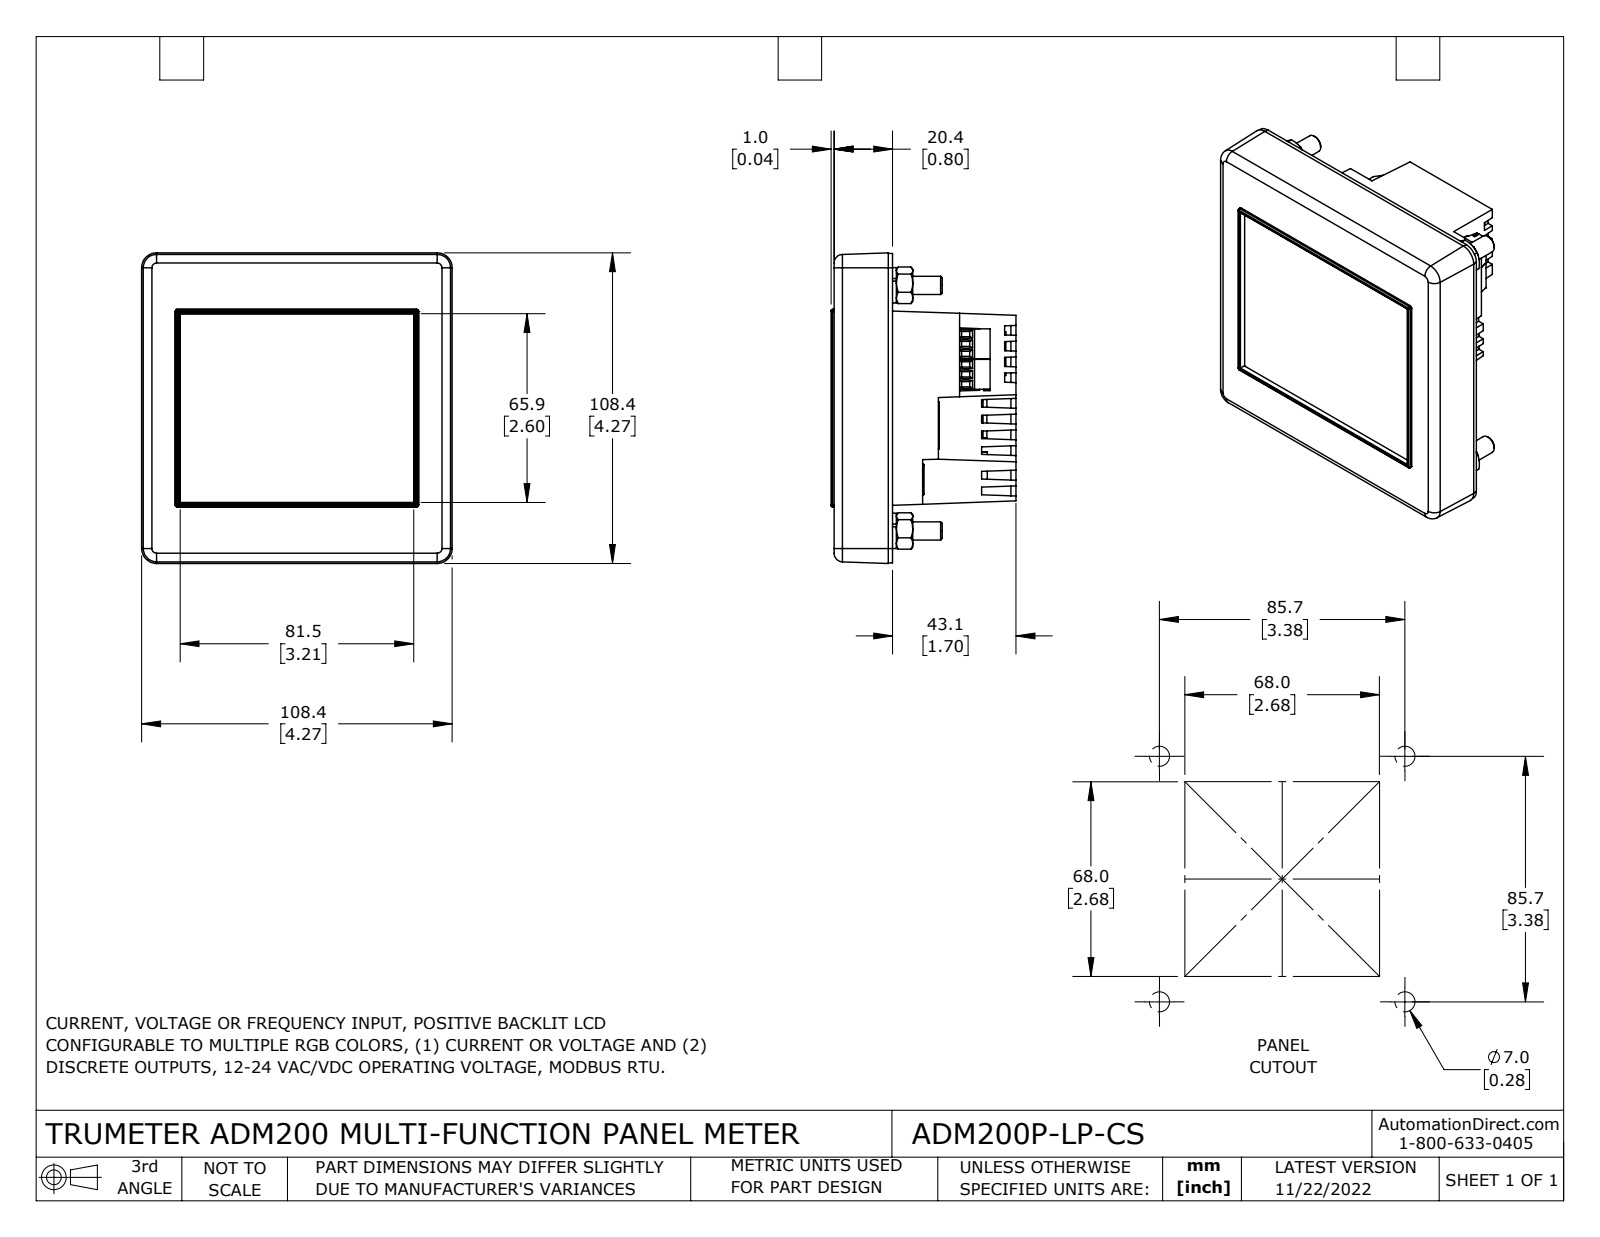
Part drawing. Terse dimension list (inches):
name: ADM200P-LP-CS
written by: SolidWorks 2021 (CONFIG_CONTROL_DESIGN)
unit: in
bodies: 23 solids, 2059 faces (1384 planar, 290 cylindrical, 385 other)
size: 4.269 × 4.269 × 2.541
volume: 7.808 in³; area: 190.8 in²
holes: 9× ⌀0.071, 6× ⌀0.114, 5× ⌀0.118, 4× ⌀0.213, 4× ⌀0.25, 4× ⌀0.26, 4× ⌀0.295, 2× ⌀0.154
bosses: 5× ⌀0.039, 4× ⌀0.487, 4× ⌀0.438, 4× ⌀0.024, 2× ⌀0.079
rounds: 32× R0.006, 30× R0.02, 7× R0.039, 4× R0.016, 4× R0.03, 4× R0.118, 4× R0.197, 2× R0.004
face distances: 0.031, 0.635, 0.11, 0.073, 0.059, 0.079, 0.694, 3.395, 3.468, 0.047
hole spacings: 0.709, 3.228, 0.136, 0.293, 0.986, 1.417, 2.126, 2.399
